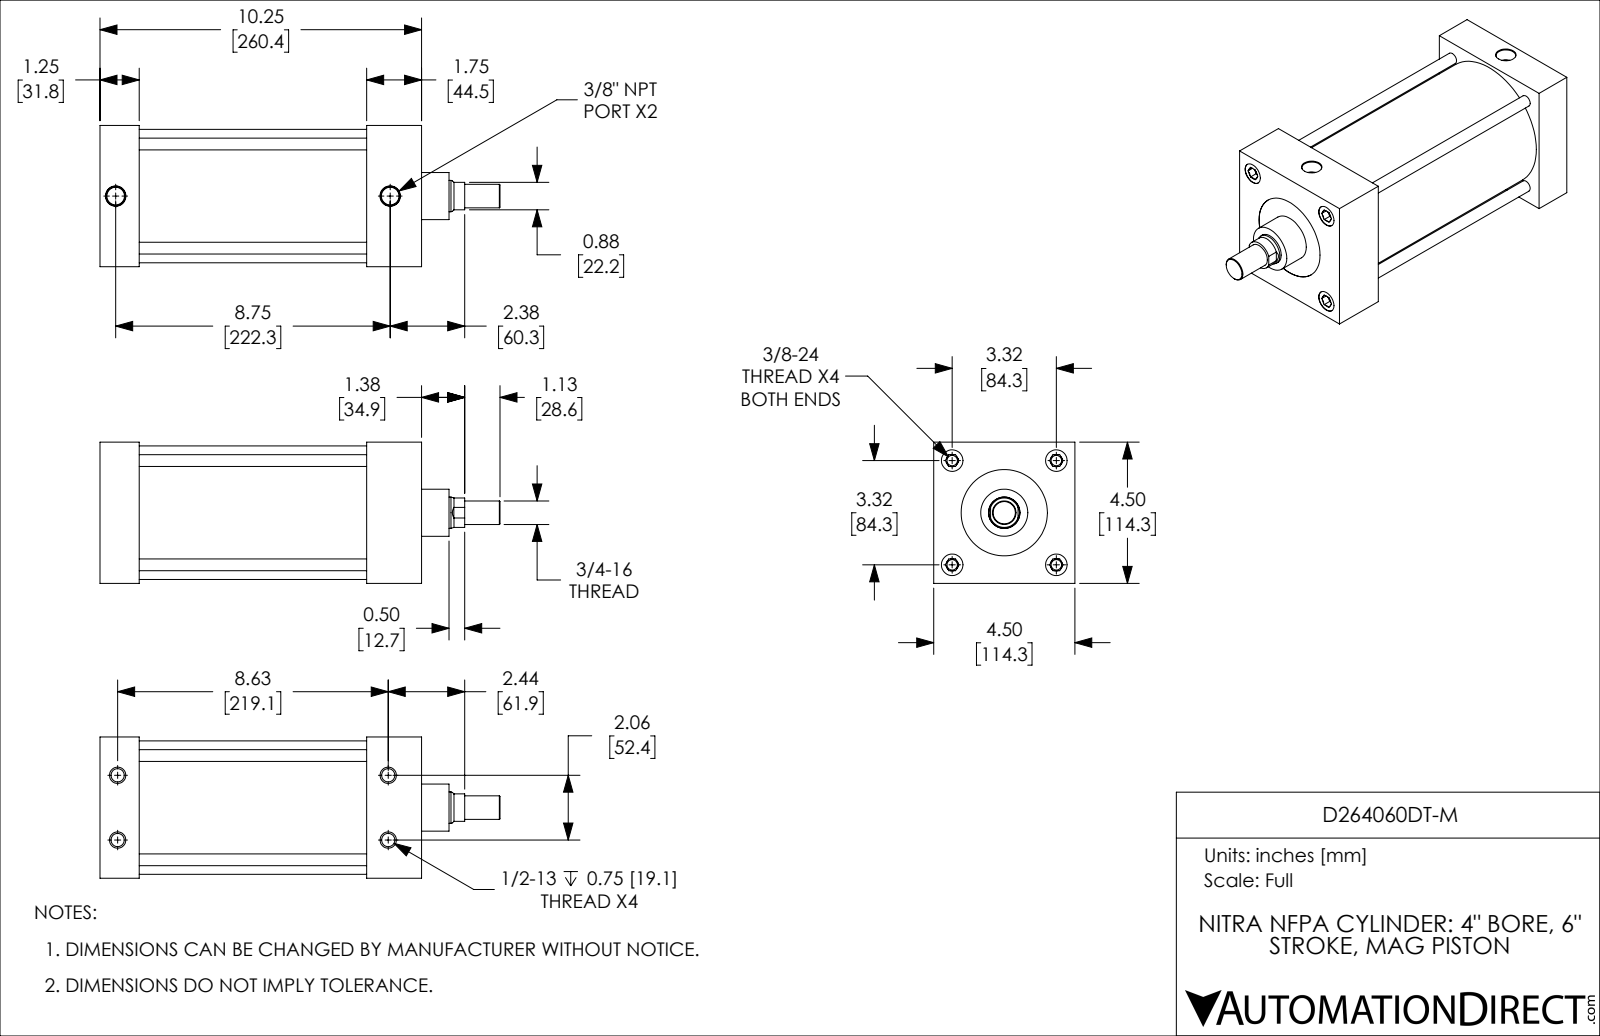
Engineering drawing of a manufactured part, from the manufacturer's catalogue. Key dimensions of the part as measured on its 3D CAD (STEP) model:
Part name (STEP PRODUCT): D264060DT-M; D264060DT-M_PISTON_KK1; D264060DT-M_BODY
STEP written by: SolidWorks 2019 (CONFIG_CONTROL_DESIGN)
Units: inches
Bodies: 2 solids, 198 faces (58 planar, 62 cylindrical, 78 other)
Overall size (bounding box): 12.75 × 4.5 × 4.5
Volume: 96.11 in³ · Surface area: 455.7 in²
Round holes (diameter × count): ⌀0.332 ×4, ⌀0.422 ×4, ⌀0.687 ×4, ⌀0.562 ×2, ⌀1.001 ×1, ⌀2.75 ×1, ⌀4.001 ×1
Round bosses / shafts (diameter × count): ⌀0.375 ×4, ⌀4.251 ×1, ⌀3.999 ×1, ⌀1.5 ×1, ⌀0.999 ×1, ⌀0.75 ×1
Partial cylindrical surfaces — rounded edges, fillets, slot ends (radius × count): R0.469 ×1
Main face-to-face distances: 1.25, 4.5, 8.5, 7.25, 10.25, 9, 1.75, 2.5, 6, 7.75
Hole centre spacings: 2.347, 3.32, 8.748, 1.033, 4.695, 8.625, 8.868, 1.034
